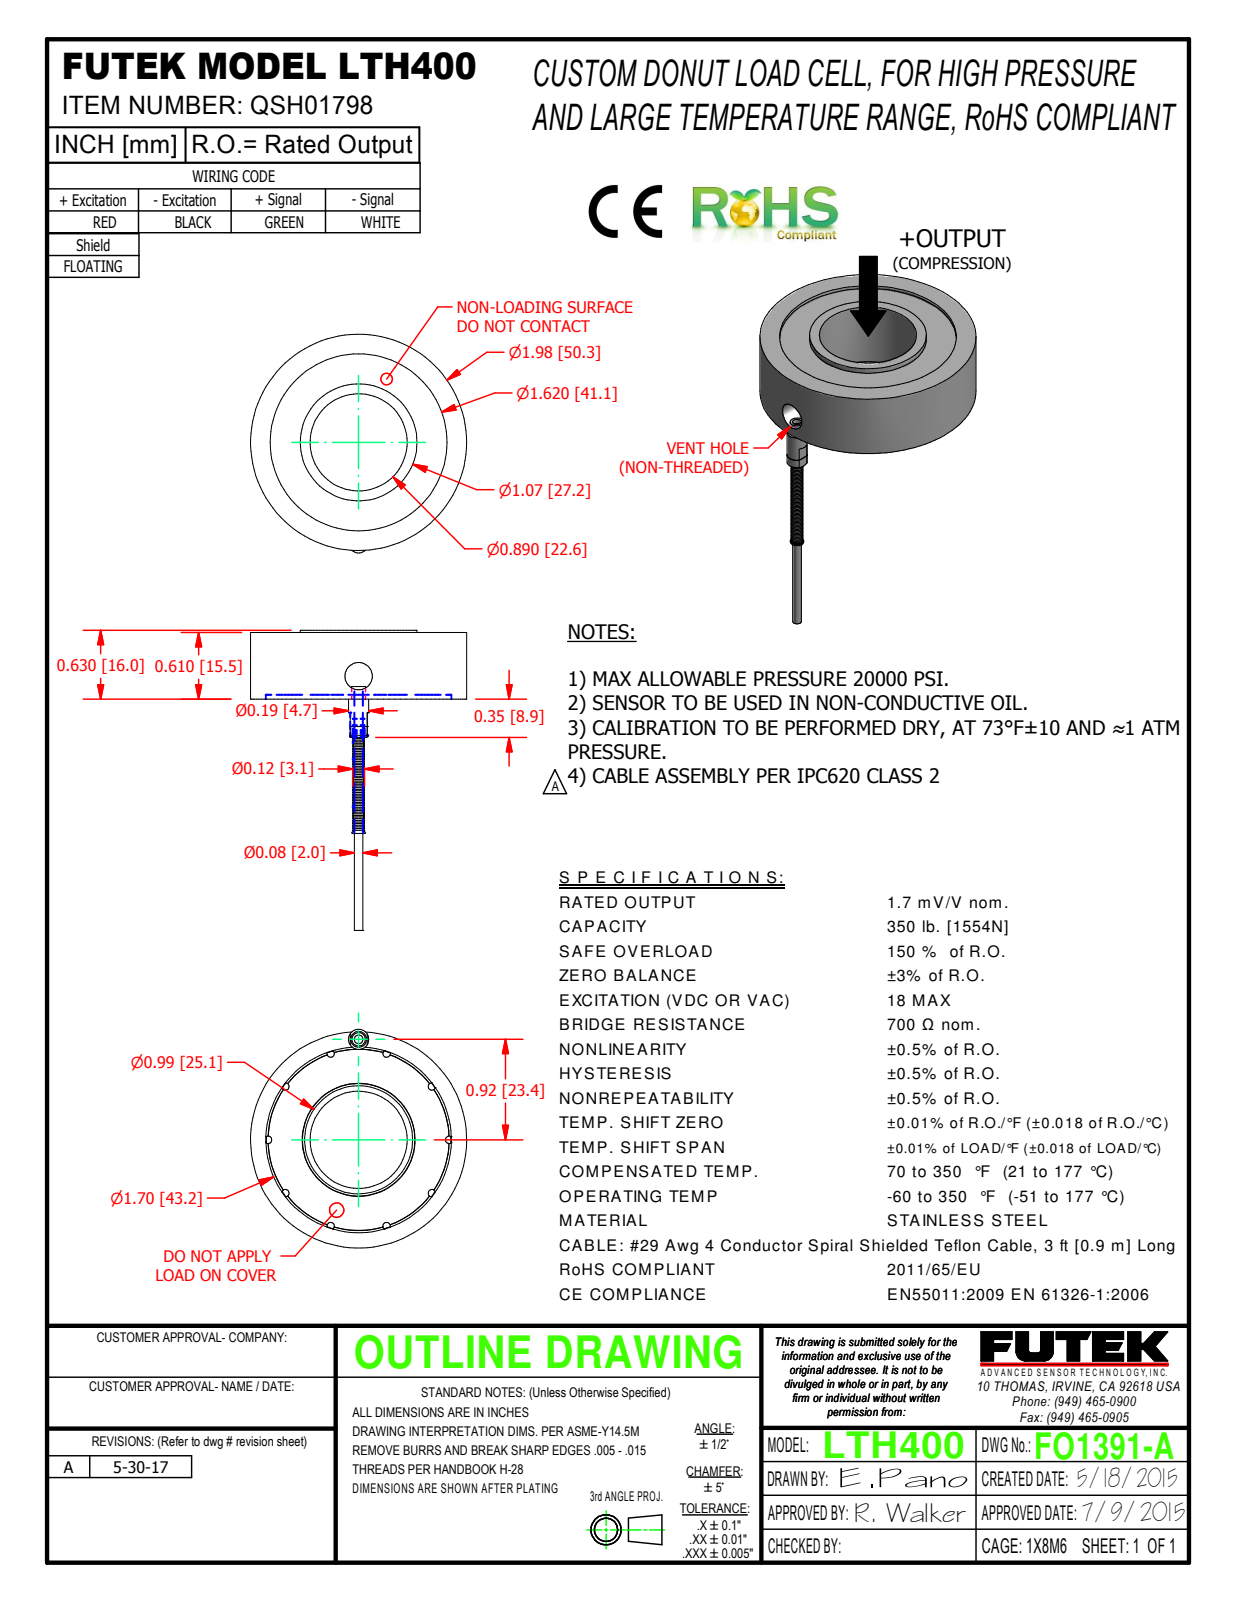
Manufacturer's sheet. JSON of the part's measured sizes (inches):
{"part_name": "QSH01798", "step_written_by": "Autodesk Inventor 2018 (AUTOMOTIVE_DESIGN)", "units": "inches", "bodies": {"solids": 1, "faces": 190, "planar": 66, "cylindrical": 27, "other": 97}, "overall_size": [2.748, 2.003, 1.98], "volume_in3": 1.417, "surface_area_in2": 12.62, "round_holes": [[0.082, 1], [0.119, 1], [0.12, 1], [0.25, 1], [0.89, 1], [1.034, 1], [1.62, 1], [1.66, 1], [1.7, 1]], "round_bosses_or_shafts": [[1.98, 1], [1.658, 1], [1.07, 1], [1.03, 1], [0.99, 1], [0.185, 1], [0.125, 1], [0.11, 1]], "face_to_face_distances": [0.54, 0.57, 0.03, 0.61, 0.04, 0.58, 0.02, 0.05, 0.63, 0.59], "hole_center_spacings": [0.92]}
